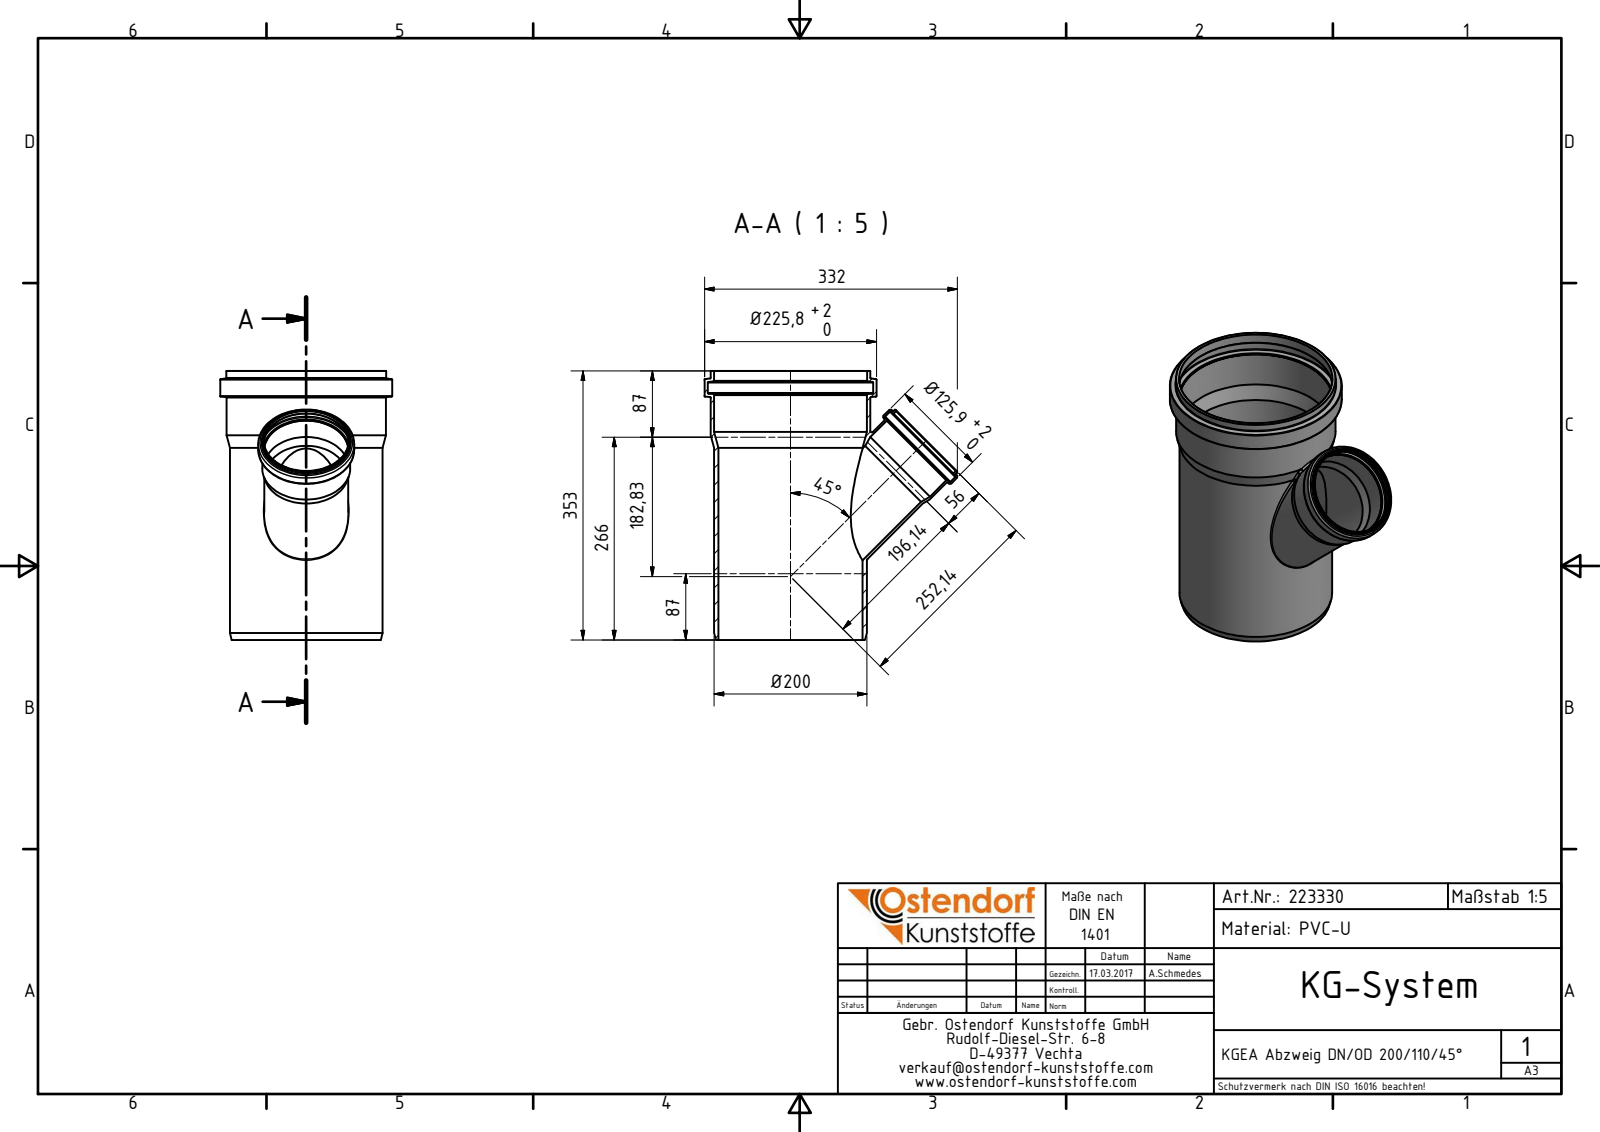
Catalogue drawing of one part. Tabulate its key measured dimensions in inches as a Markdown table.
| quantity | value |
| --- | --- |
| part name | 223330 KGEA Abzweig DN_OD 200_110_45° |
| STEP written by | Autodesk Inventor 2016 (AUTOMOTIVE_DESIGN) |
| units | inches |
| bodies | 1 solid, 64 faces (5 planar, 18 cylindrical, 41 other) |
| overall size | 13.898 × 13.071 × 8.89 |
| volume | 77.01 in³ |
| surface area | 820.4 in² |
| round holes (diameter × count) | 4.37 × 2, 4.087 × 1, 4.358 × 1, 4.768 × 1, 7.453 × 1, 7.898 × 1, 7.909 × 1, 8.543 × 1 |
| round bosses / shafts (diameter × count) | 8.89 × 1, 8.256 × 1, 8.244 × 1, 7.894 × 1, 4.957 × 1, 4.559 × 1, 4.547 × 1, 4.339 × 1 |
| main face-to-face distances | 13.898, 12.647, 1.251, 0.717 |
